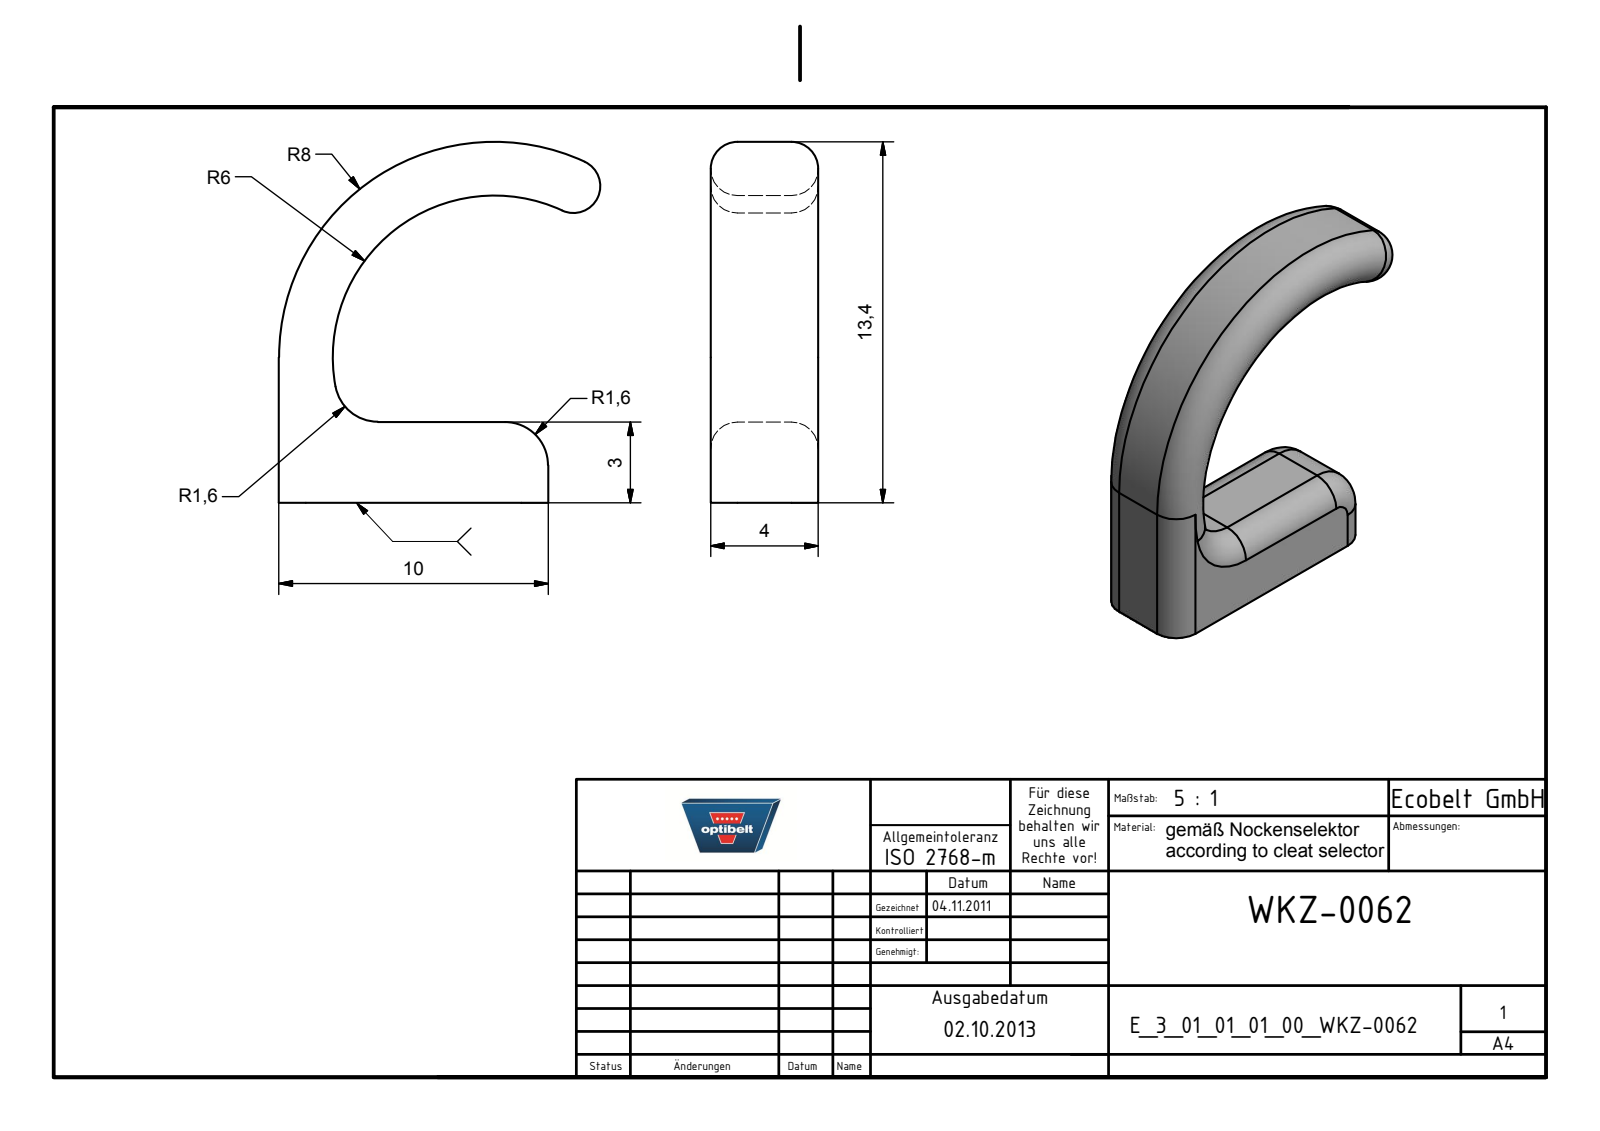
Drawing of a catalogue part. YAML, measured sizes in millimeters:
part_name: "E_3_01_01_01_00_WKZ-0062"
step_written_by: "Autodesk Inventor 2021 (AUTOMOTIVE_DESIGN)"
units: millimeters
bodies: {solids: 1, faces: 25, planar: 6, cylindrical: 11, other: 8}
overall_size: [13.4, 11.94, 4]
volume: 238
surface_area: 320
partial_cylinders:
  - {radius: 1, count: 7}
  - {radius: 1.6, count: 2}
  - {radius: 6, count: 1}
  - {radius: 8, count: 1}
face_to_face_distances: [4, 3, 10]
